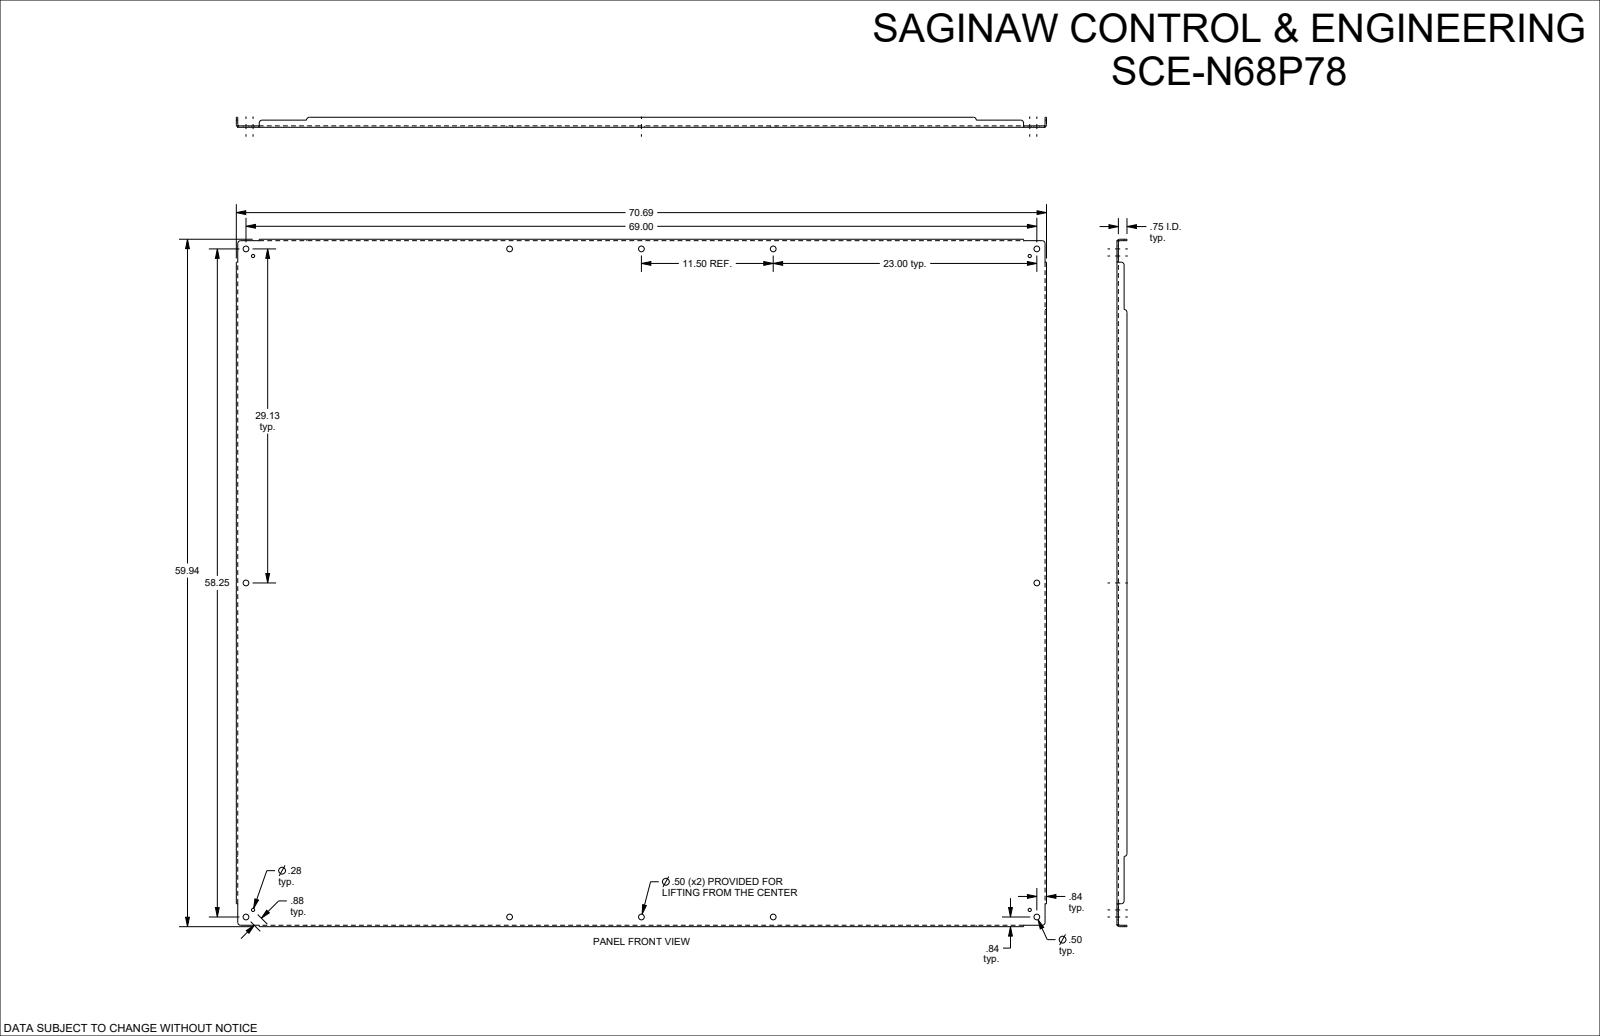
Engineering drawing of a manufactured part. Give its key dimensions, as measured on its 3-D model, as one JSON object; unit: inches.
{"part_name": "SCE-N68P78", "step_written_by": "SolidWorks 2023 (AUTOMOTIVE_DESIGN)", "units": "inches", "bodies": {"solids": 1, "faces": 130, "planar": 46, "cylindrical": 60, "other": 24}, "overall_size": [70.688, 59.938, 0.875], "volume_in3": 548.7, "surface_area_in2": 8815, "round_holes": [[0.5, 12], [0.281, 4]], "partial_cylinders_radius": [[0.25, 12], [0.112, 4], [0.237, 4]], "face_to_face_distances": [0.125, 0.125, 59.813, 70.563, 59.687, 59.938, 70.438, 70.687, 0.75, 0.875], "hole_center_spacings": [23, 62.626, 58.25, 0.875, 11.5, 22.39, 28.513, 29.125]}
